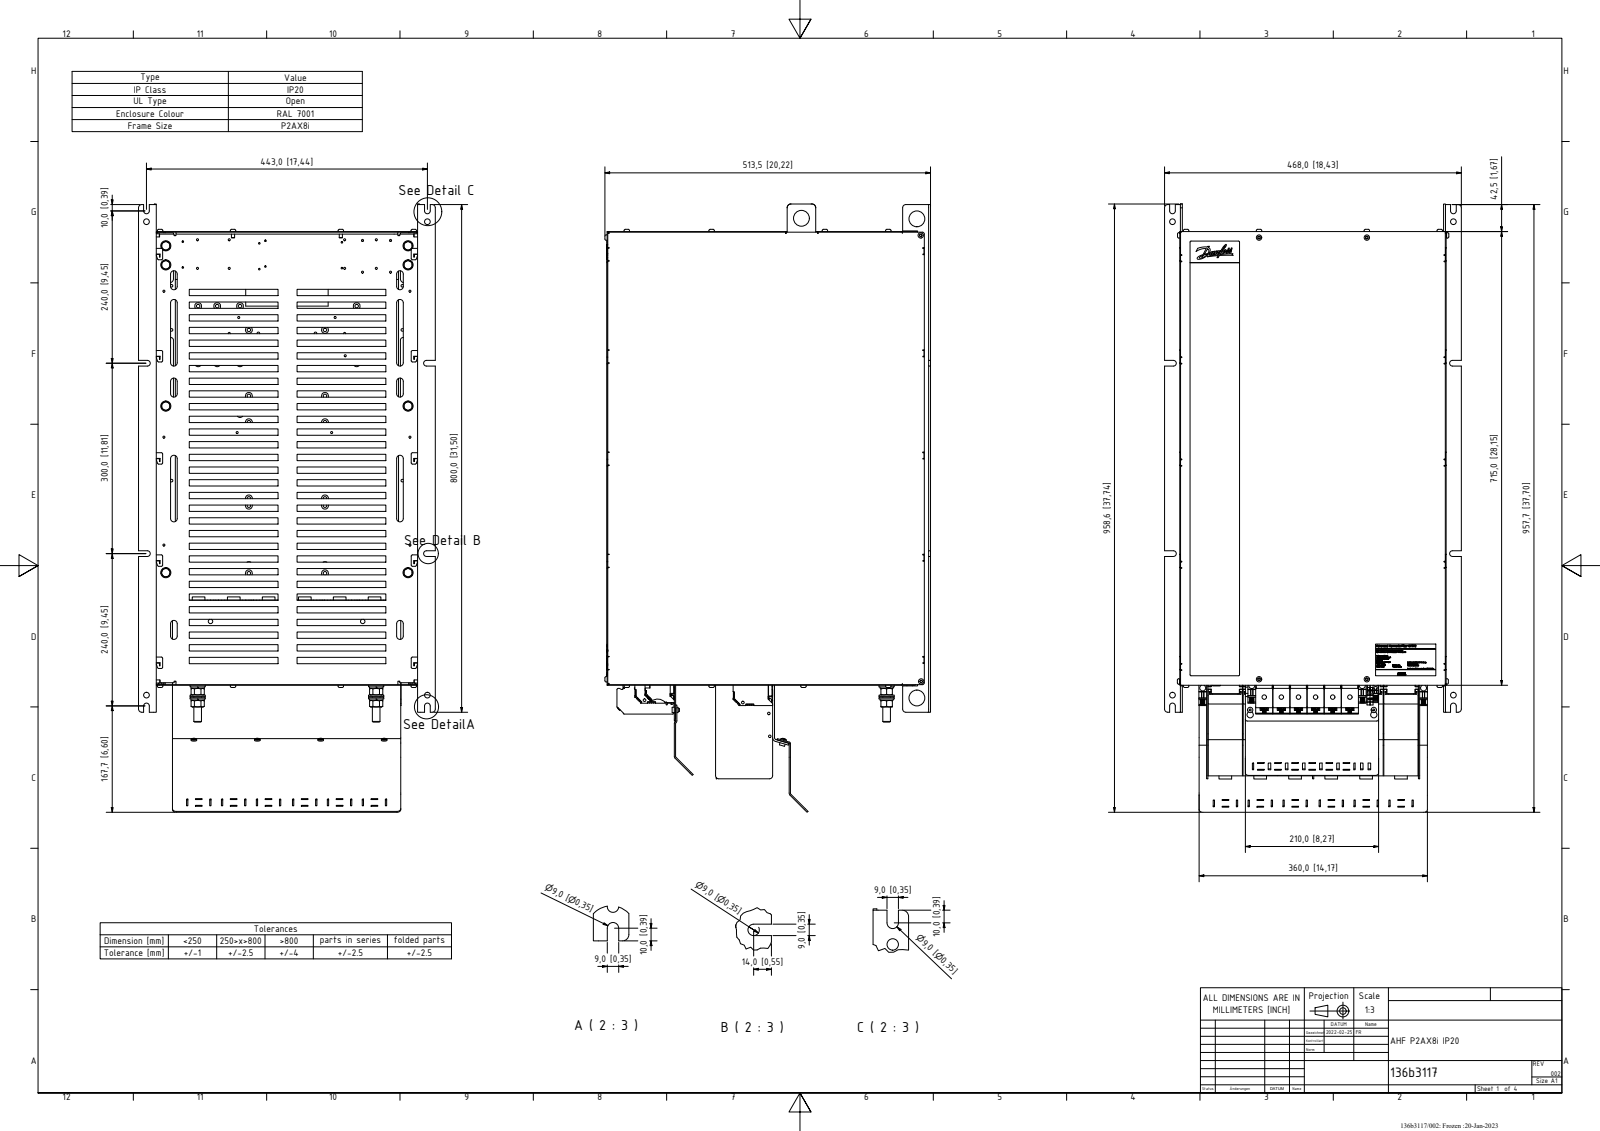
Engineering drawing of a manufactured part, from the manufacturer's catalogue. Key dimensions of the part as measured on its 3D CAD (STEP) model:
Part name (STEP PRODUCT): X8_IP20_IF_OUT
STEP written by: CREO PARAMETRIC BY PTC INC, 2020342 (CONFIG_CONTROL_DESIGN)
Units: millimetres
Bodies: 8 solids, 2471 faces (1748 planar, 667 cylindrical, 56 other)
Overall size (bounding box): 958.56 × 513.5 × 468
Volume: 9 084 000 mm³ · Surface area: 4 256 000 mm²
Round holes (diameter × count): ⌀7 ×6, ⌀9 ×4, ⌀25 ×3, ⌀12.5 ×2, ⌀76 ×2, ⌀90 ×2, ⌀104 ×2, ⌀34 ×1, ⌀48 ×1, ⌀62 ×1
Round bosses / shafts (diameter × count): ⌀8.5 ×17, ⌀13 ×7, ⌀30 ×6, ⌀16 ×6, ⌀26.73 ×3, ⌀107 ×2, ⌀93 ×2, ⌀79 ×2
Partial cylindrical surfaces — rounded edges, fillets, slot ends (radius × count): R2 ×258, R4.5 ×8, R1 ×4, R3 ×4, R1.5 ×2, R11.5 ×2, R61.4 ×2, R15.05 ×1
Main face-to-face distances: 4, 416, 3, 412, 420, 2, 484, 482, 712, 487
Hole centre spacings: 27, 54, 81, 108, 443, 746, 867.62, 135
